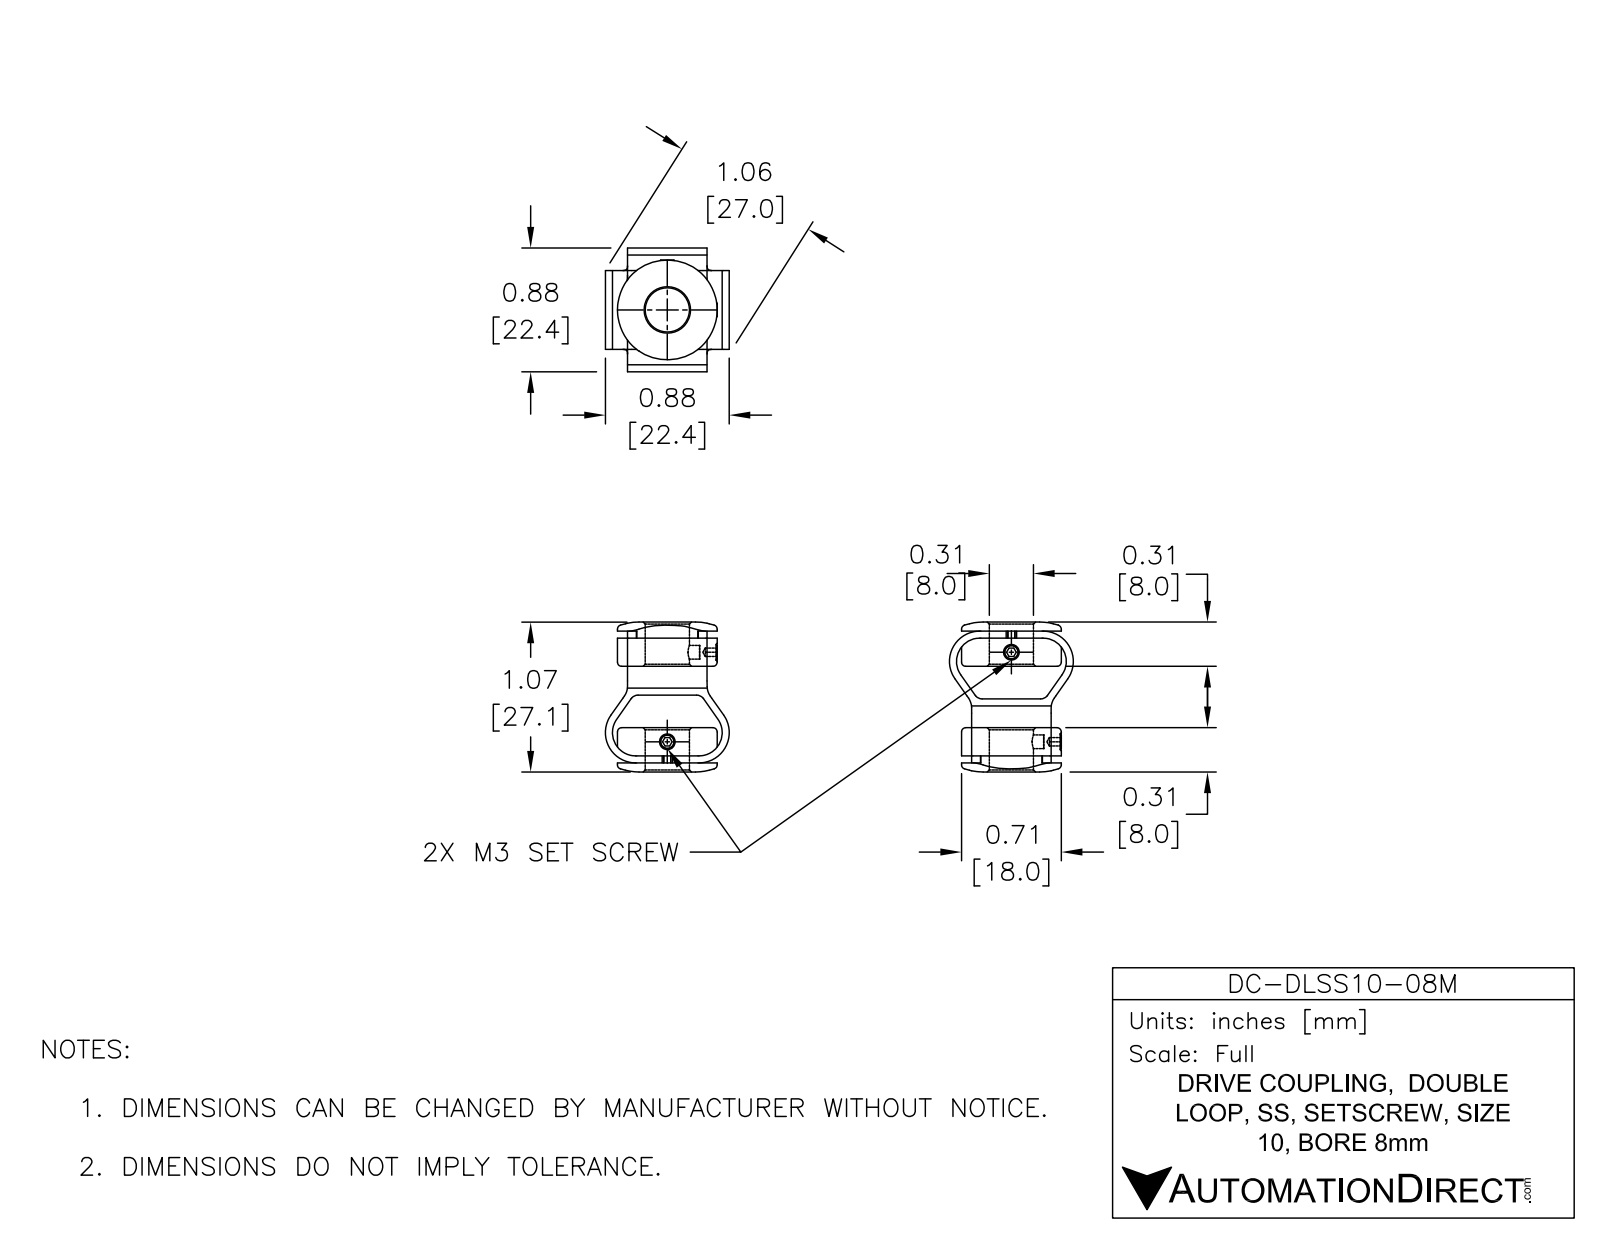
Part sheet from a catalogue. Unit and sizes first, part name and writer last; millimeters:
Units: millimetres
Overall size (bounding box): 33.4 × 22.35 × 22.35
Round holes (diameter × count): ⌀8 ×1
Round bosses / shafts (diameter × count): ⌀18.01 ×1
Partial cylindrical surfaces — rounded edges, fillets, slot ends (radius × count): R4.19 ×4, R5.46 ×4, R5.59 ×1
Main face-to-face distances: 1.27, 16.38, 17.02, 17.65, 33.4, 15.75, 12.23, 11.6, 5.42, 27.98
Volume: 3 882 mm³ · Surface area: 3 960 mm²
Bodies: 1 solid, 110 faces (57 planar, 28 cylindrical, 25 other)
Part name (STEP PRODUCT): DC-DLSS10-08M
STEP written by: SolidWorks 2015 (AUTOMOTIVE_DESIGN)
